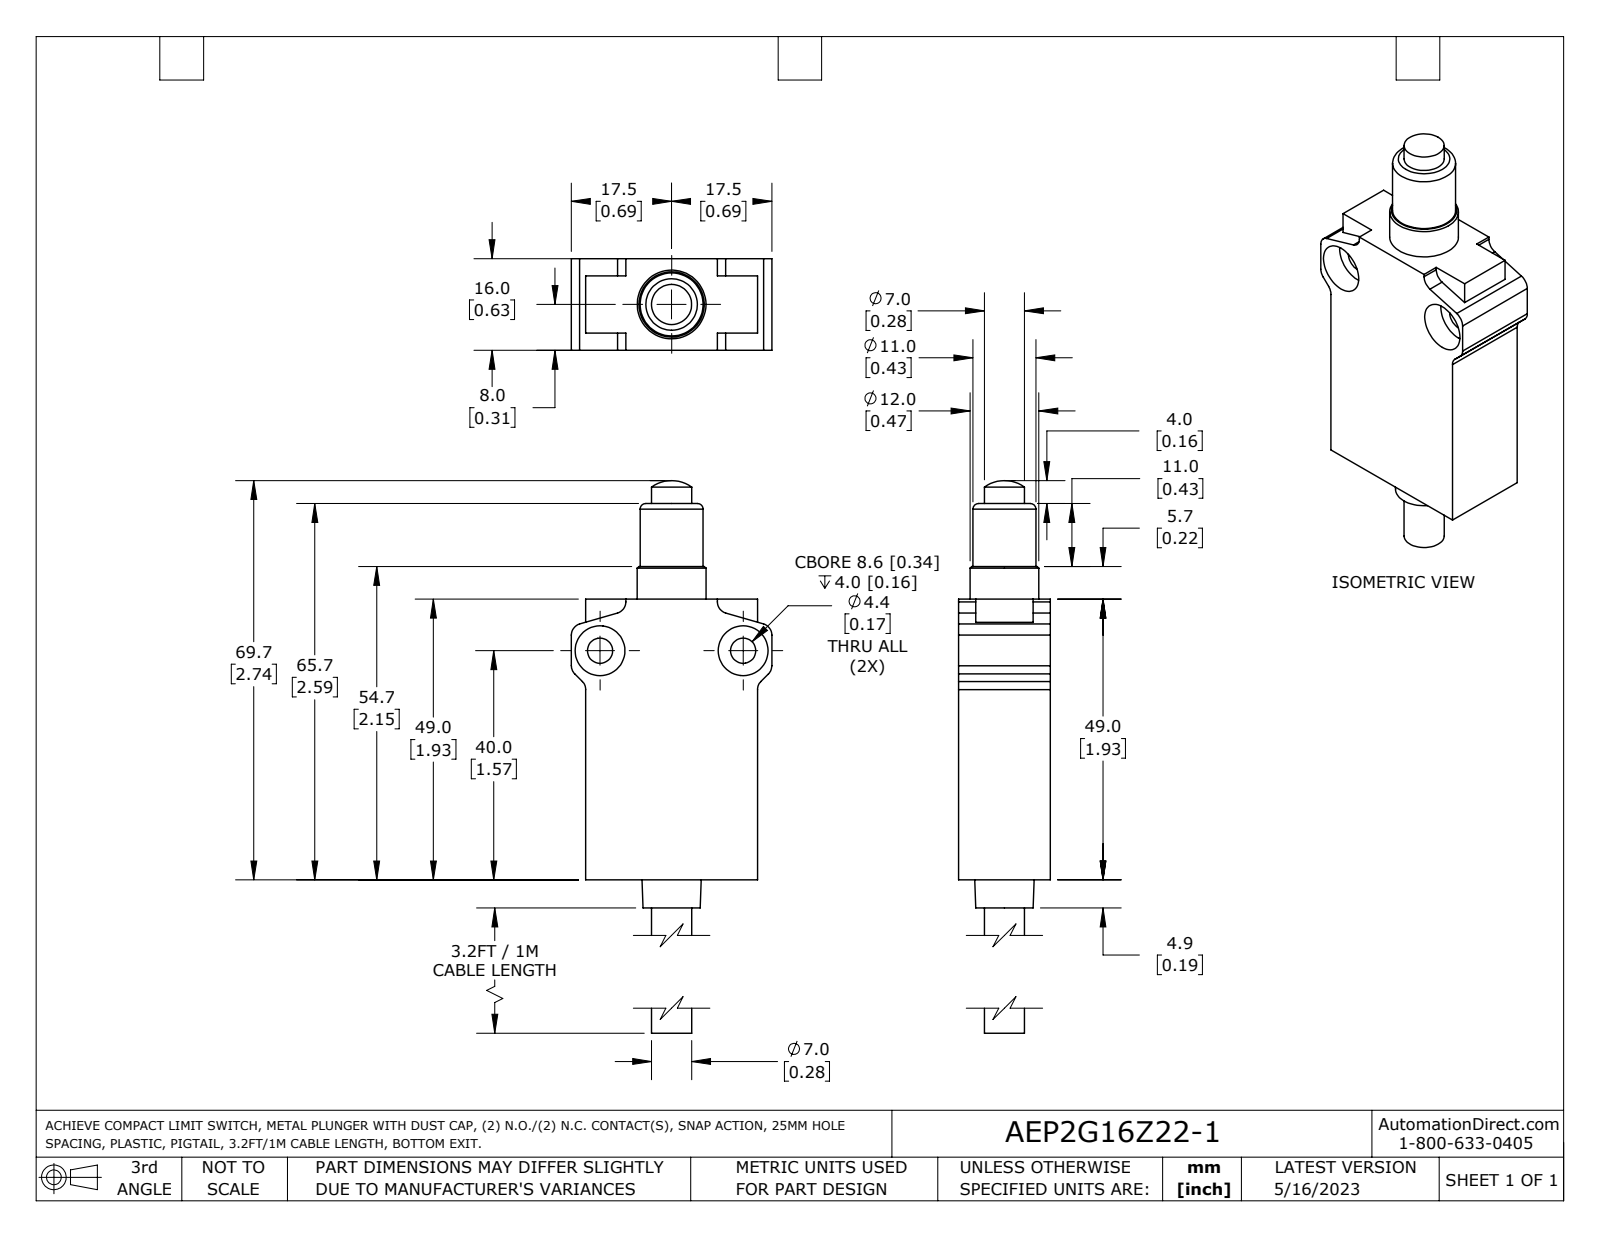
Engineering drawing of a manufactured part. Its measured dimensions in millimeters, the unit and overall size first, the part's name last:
Units: millimetres
Overall size (bounding box): 84.6 × 35 × 16
Round holes (diameter × count): ⌀4.4 ×2, ⌀8.7 ×2, ⌀7.1 ×1
Round bosses / shafts (diameter × count): ⌀12 ×1, ⌀11 ×1, ⌀7 ×1, ⌀5 ×1
Partial cylindrical surfaces — rounded edges, fillets, slot ends (radius × count): R2 ×8, R6.5 ×1
Main face-to-face distances: 16, 30, 49, 12, 4, 2.5, 32.5, 1, 8, 35
Hole centre spacings: 25
Volume: 25 190 mm³ · Surface area: 8 135 mm²
Bodies: 1 solid, 81 faces (46 planar, 27 cylindrical, 8 other)
Part name (STEP PRODUCT): AEP2G16Z22-1
STEP written by: SolidWorks 2021 (AUTOMOTIVE_DESIGN)
